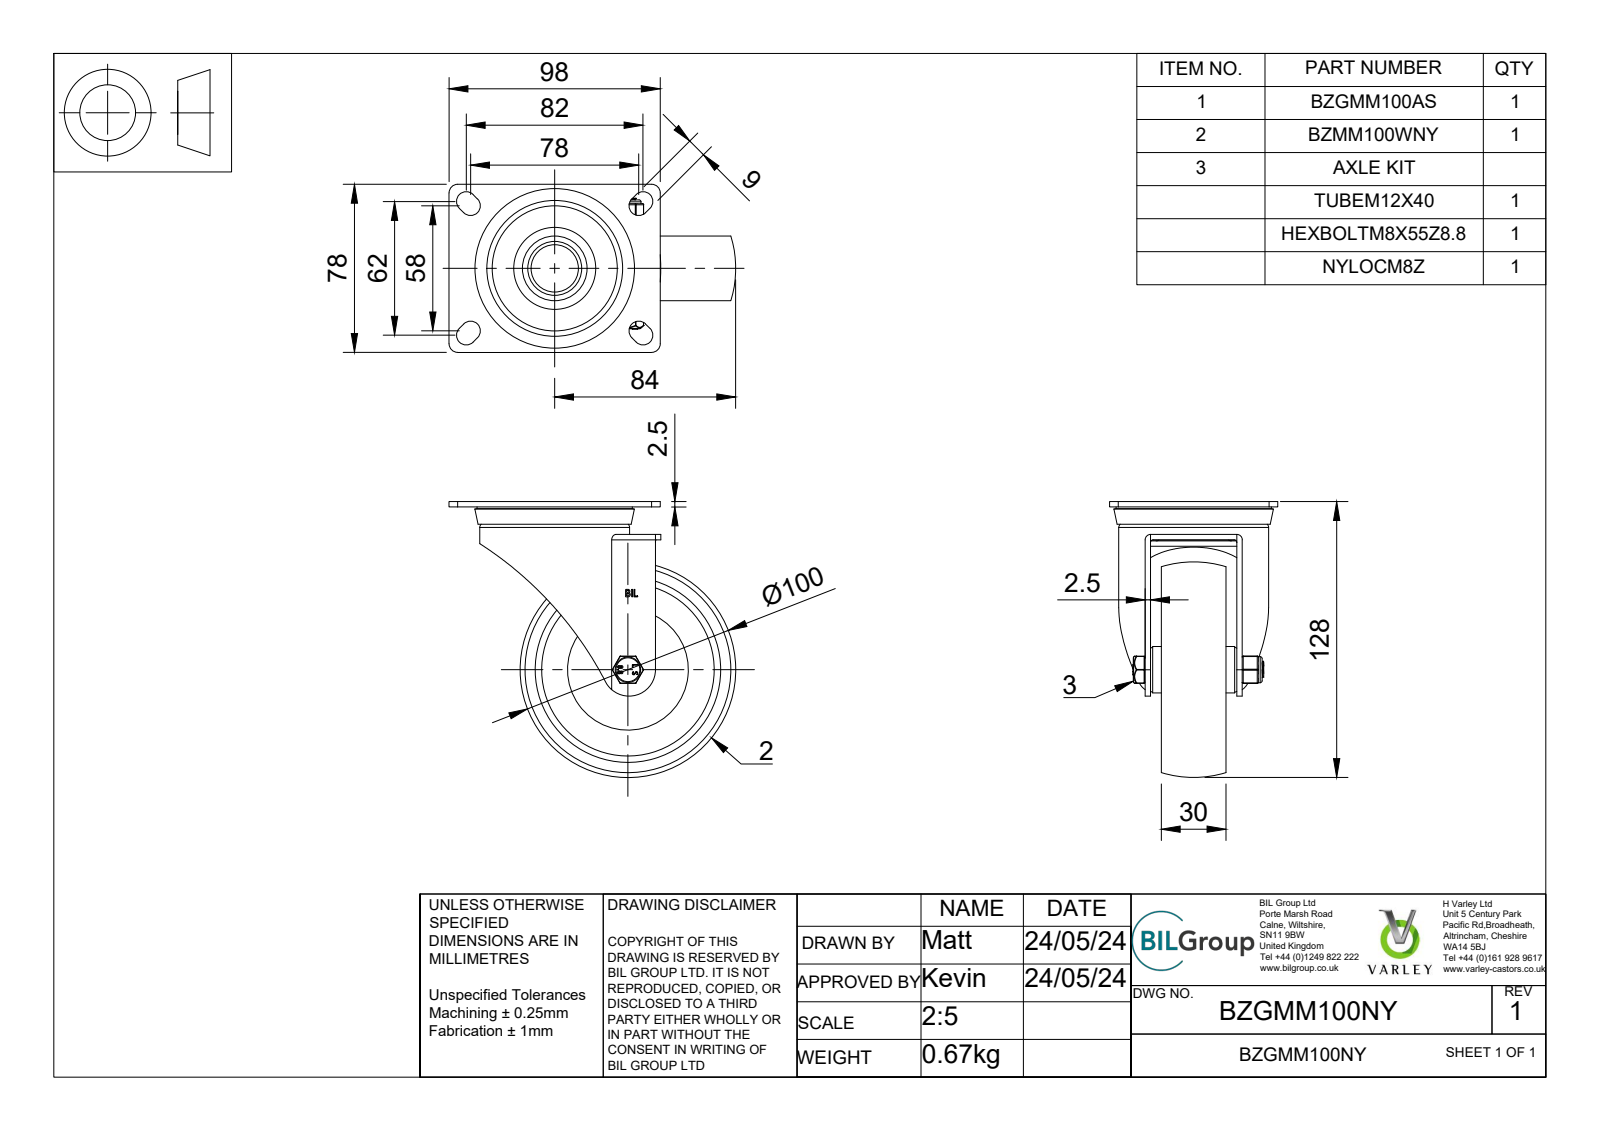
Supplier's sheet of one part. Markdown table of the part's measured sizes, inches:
| quantity | value |
| --- | --- |
| part name | BZGMM100NY v5; BZMM100WNY v1; NYLON WHEEL; TUBEM12X40 v1 (+8 more) |
| STEP written by | Autodesk Translation Framework v13.14.0.145 (AUTOMOTIVE_DESIGN) |
| units | inches |
| bodies | 36 solids, 378 faces (124 planar, 136 cylindrical, 118 other) |
| overall size | 5.236 × 5.039 × 3.071 |
| volume | 10.54 in³ |
| surface area | 145.6 in² |
| round holes (diameter × count) | 0.026 × 2, 0.315 × 1, 0.323 × 1, 0.331 × 1, 0.339 × 1, 0.488 × 1, 1.024 × 1, 1.181 × 1, 2.539 × 1, 3.386 × 1 |
| round bosses / shafts (diameter × count) | 2.736 × 1, 1.85 × 1, 0.984 × 1, 0.846 × 1, 0.476 × 1, 0.469 × 1, 0.453 × 1, 0.31 × 1 |
| partial cylindrical surfaces (radius × count) | 0.02 × 18, 0.01 × 12, 0.177 × 8, 0.013 × 4, 0.025 × 4, 0.049 × 4, 0.157 × 4, 0.025 × 2 |
| main face-to-face distances | 0.098, 0.295, 0.157, 0.709, 0.866, 0.197, 0.807, 0.965, 1.673, 0.512 |
| hole center spacings | 0.127, 0.098 |
